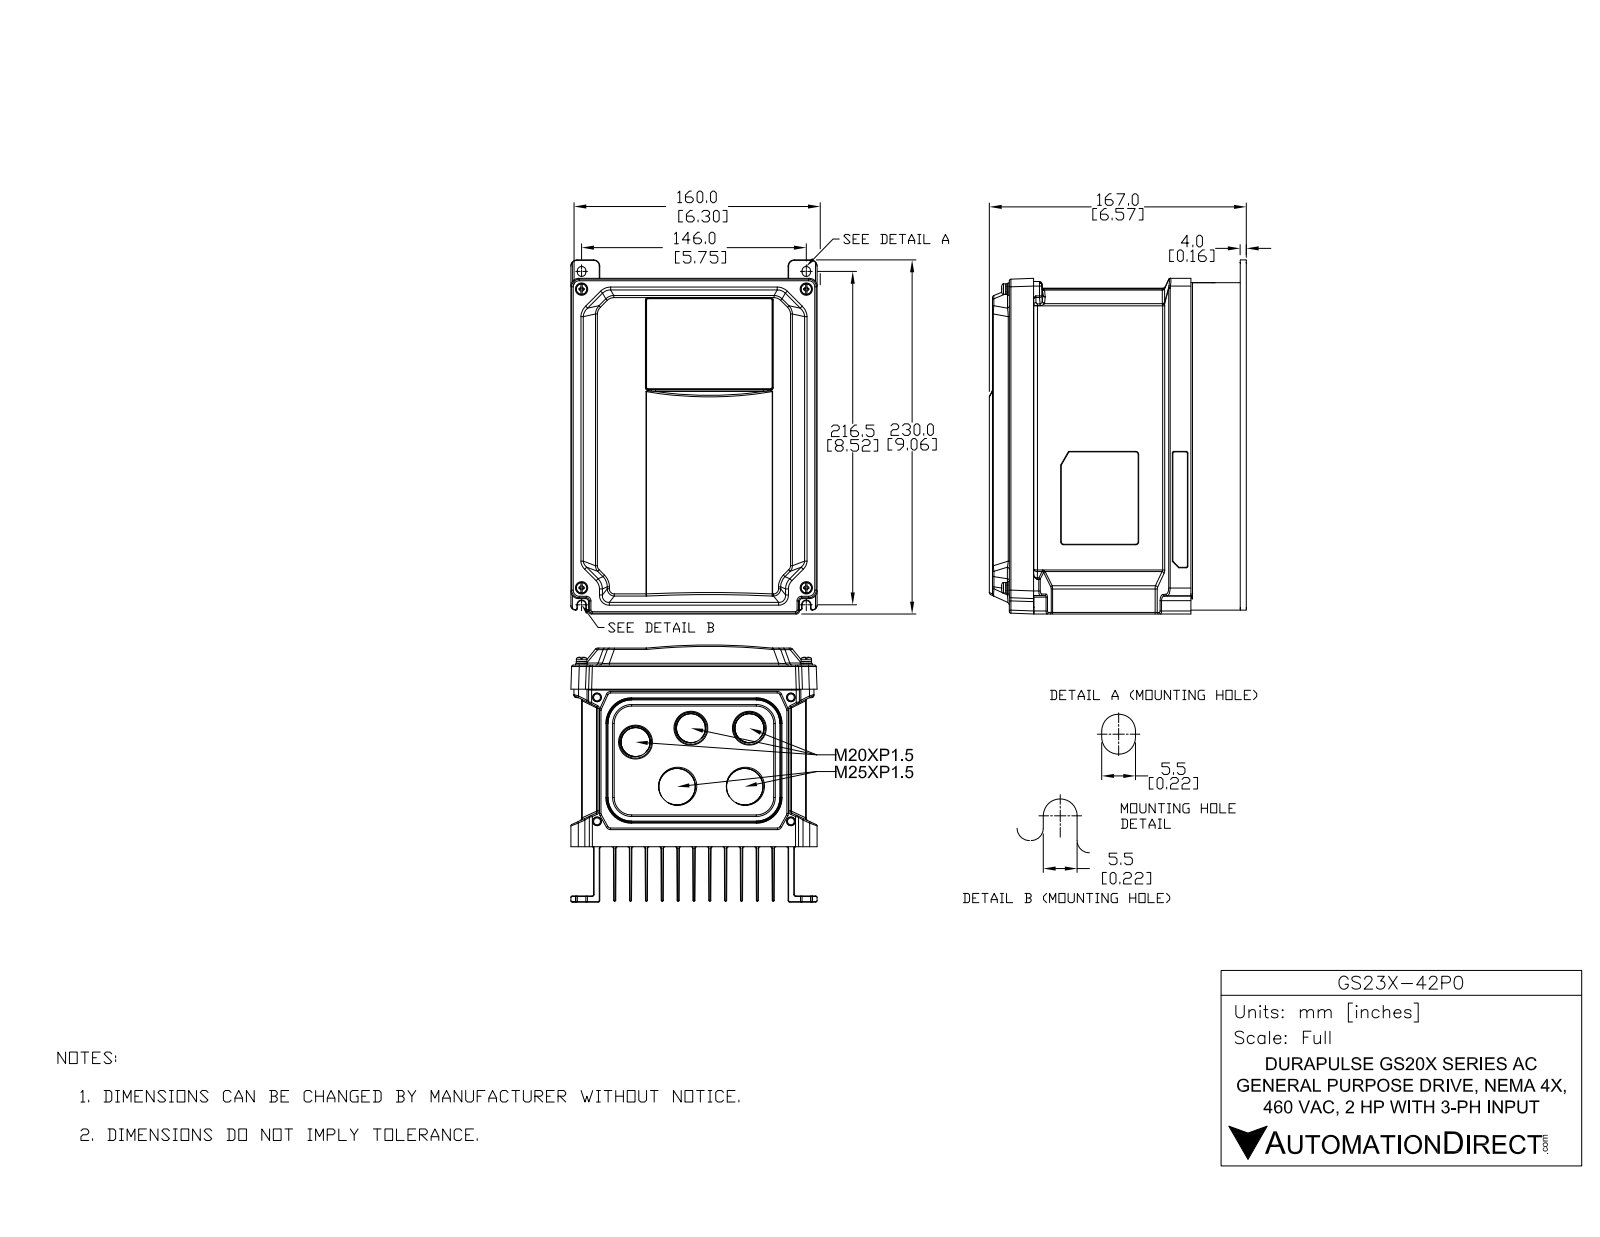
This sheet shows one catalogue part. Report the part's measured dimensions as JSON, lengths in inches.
{"part_name": "VFD-MS300-NEMA4X-A2(VFD4A2MS43MFSAA)(VFD4A2MS43MNSAA)(VFD7A5MS23MNSAA)-PD-3D01 R1b", "step_written_by": "SolidWorks 2017 (AUTOMOTIVE_DESIGN)", "units": "inches", "bodies": {"solids": 11, "faces": 3937, "planar": 2350, "cylindrical": 834, "other": 753}, "overall_size": [9.26, 6.575, 6.299], "volume_in3": 57.56, "surface_area_in2": 944.1, "round_holes": [[0.098, 7], [0.165, 4], [0.591, 3], [0.822, 3], [0.827, 3], [0.13, 2], [0.15, 2], [1.015, 2]], "round_bosses_or_shafts": [[0.988, 3], [0.929, 3], [0.78, 3]], "partial_cylinders_radius": [[0.039, 162], [0.02, 91], [0.012, 84], [0.059, 66], [0.079, 40], [0.118, 28], [0.197, 17], [0.004, 14]], "face_to_face_distances": [0.406, 0.811, 1.217, 1.622, 2.028, 2.433, 2.839, 3.244, 0.394, 3.65], "hole_center_spacings": [0.236, 3.15, 4.961, 6.339, 8.049, 0.472, 0.495, 0.539]}
